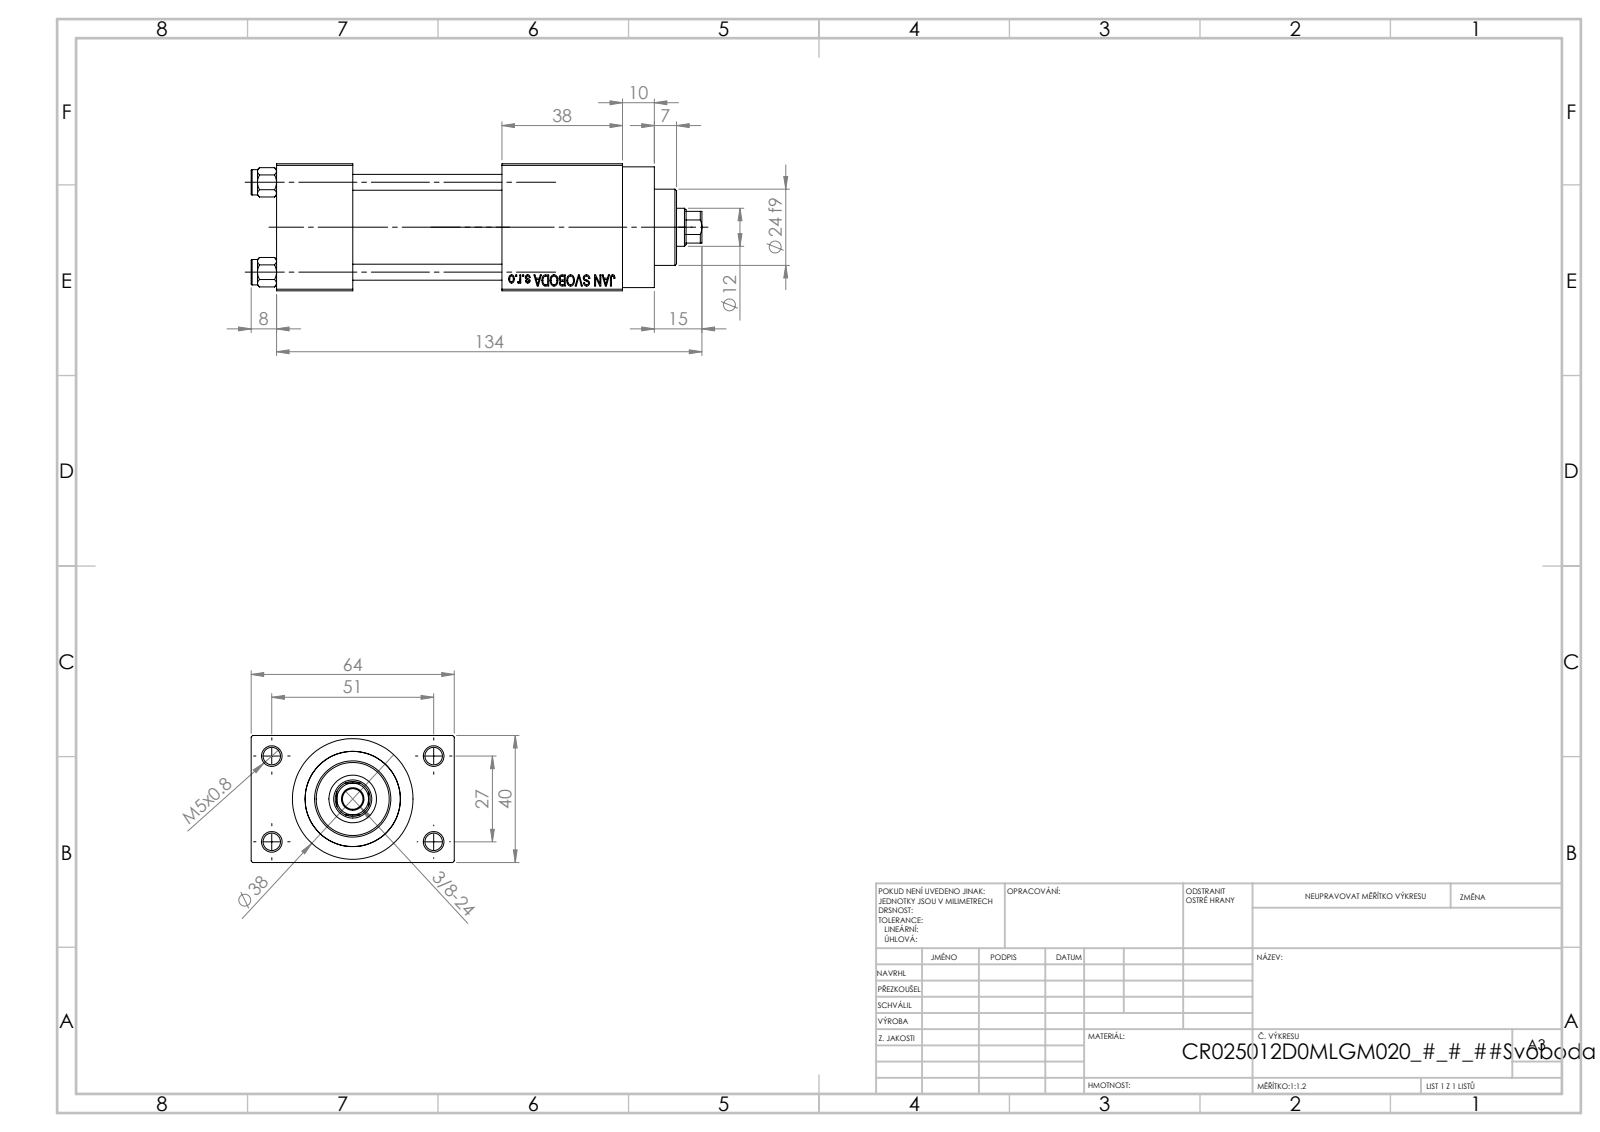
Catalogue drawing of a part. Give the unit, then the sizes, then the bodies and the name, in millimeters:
Units: millimetres
Overall size (bounding box): 142 × 64 × 40
Round holes (diameter × count): ⌀5 ×4, ⌀5.5 ×4, ⌀20 ×3, ⌀7 ×2, ⌀13.16 ×2, ⌀6.5 ×1, ⌀12 ×1, ⌀15 ×1, ⌀25 ×1, ⌀30 ×1
Round bosses / shafts (diameter × count): ⌀8 ×4, ⌀38 ×1, ⌀31 ×1, ⌀24 ×1
Partial cylindrical surfaces — rounded edges, fillets, slot ends (radius × count): R5.5 ×1
Main face-to-face distances: 40, 12, 52, 47, 24, 71, 64, 38, 109, 85
Hole centre spacings: 11.37, 20.01, 28.3, 28.85, 29.89, 39.66, 48.34, 27
Volume: 175 245 mm³ · Surface area: 61 663 mm²
Bodies: 11 solids, 1103 faces (496 planar, 89 cylindrical, 518 other)
Part name (STEP PRODUCT): V215CR_VCP_D; V215_VC_A; NUT_M5_D; V215CR_D_Body (+1 more)
STEP written by: SolidWorks 2019 (CONFIG_CONTROL_DESIGN)
